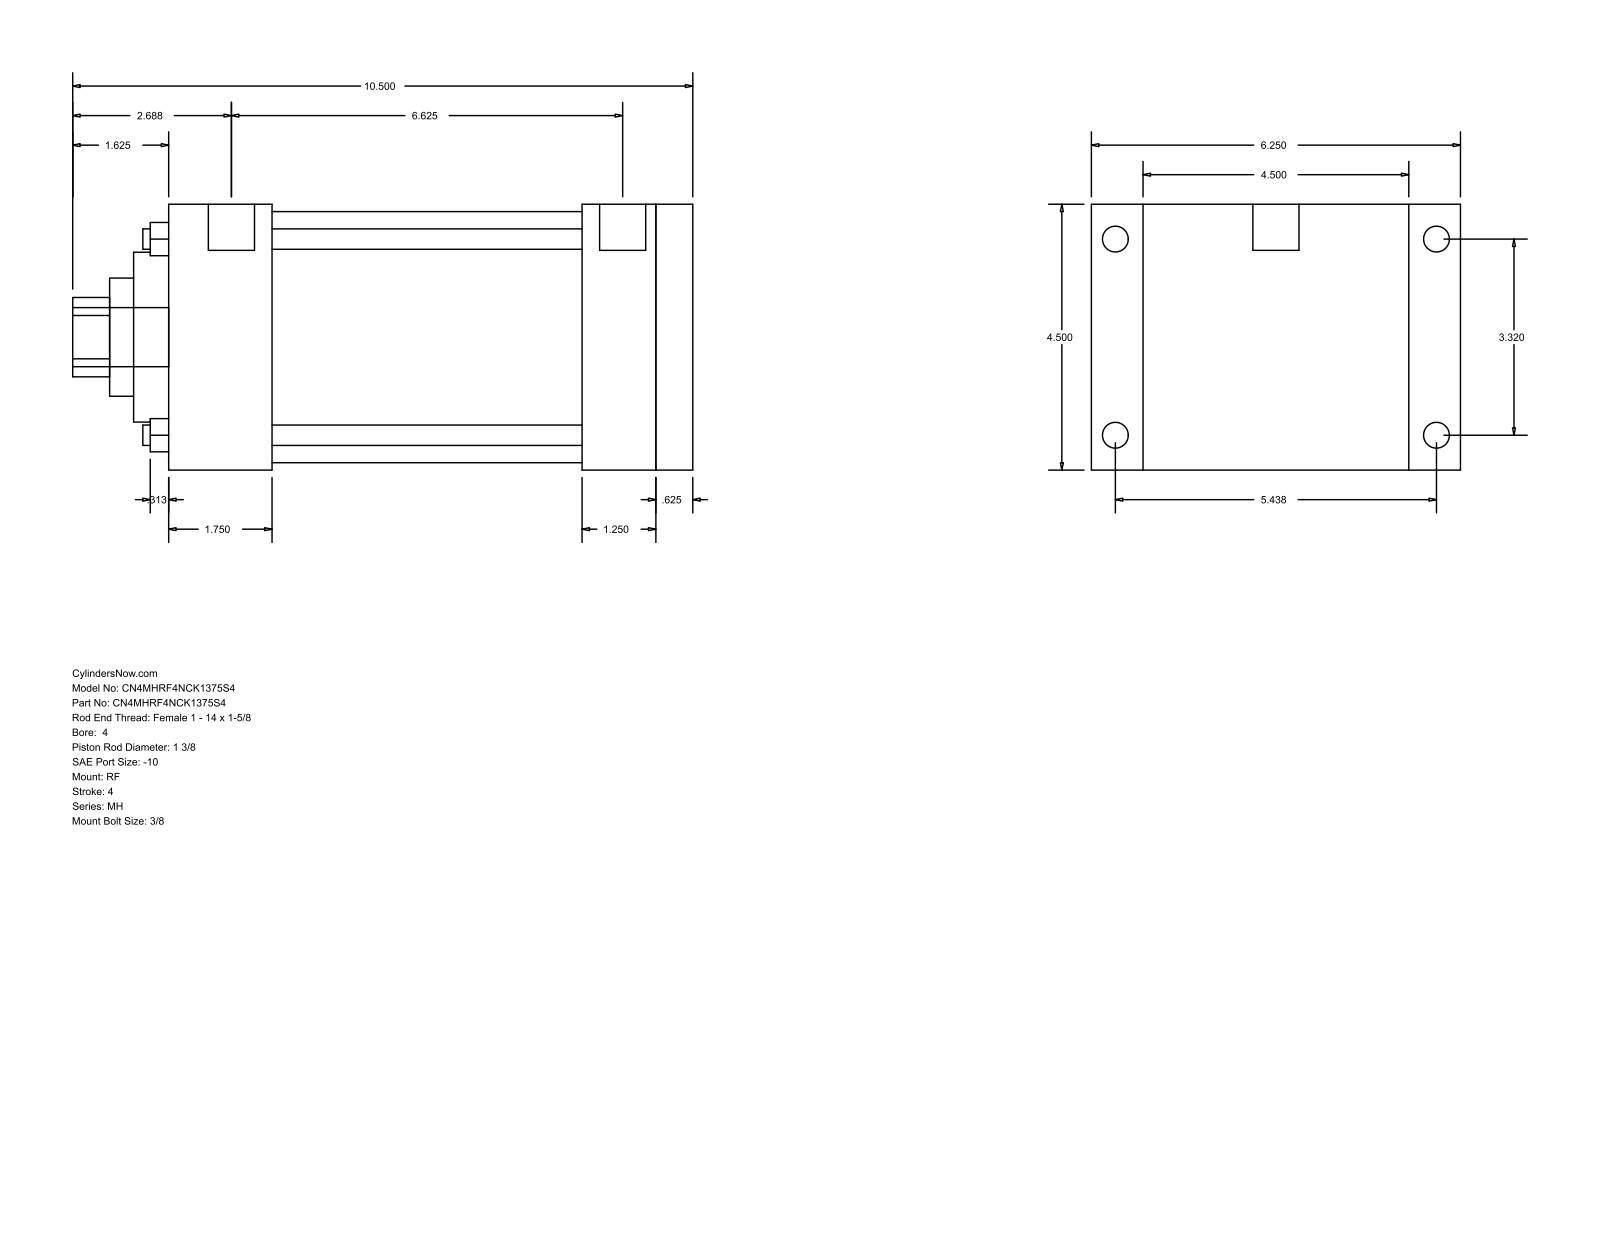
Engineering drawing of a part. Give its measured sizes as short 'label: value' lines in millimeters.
name: MH_RF__0400_1.375
written by: GSSL Pune (CONFIG_CONTROL_DESIGN)
unit: mm
bodies: 0 solids, 94 faces (65 planar, 29 cylindrical, 0 other)
size: 266.7 × 158.75 × 114.3
holes: 4× ⌀8.76, 1× ⌀34.92, 1× ⌀50.8, 1× ⌀73.03, 1× ⌀107.95
bosses: 4× ⌀11.13, 4× ⌀8.73, 2× ⌀19.84, 1× ⌀25.4
rounds: 1× R17.06
face distances: 114.3, 225.43, 15.88, 209.55, 44.45, 165.1, 180.98, 177.8, 133.35, 31.75
hole spacings: 59.62, 84.32, 119.25
